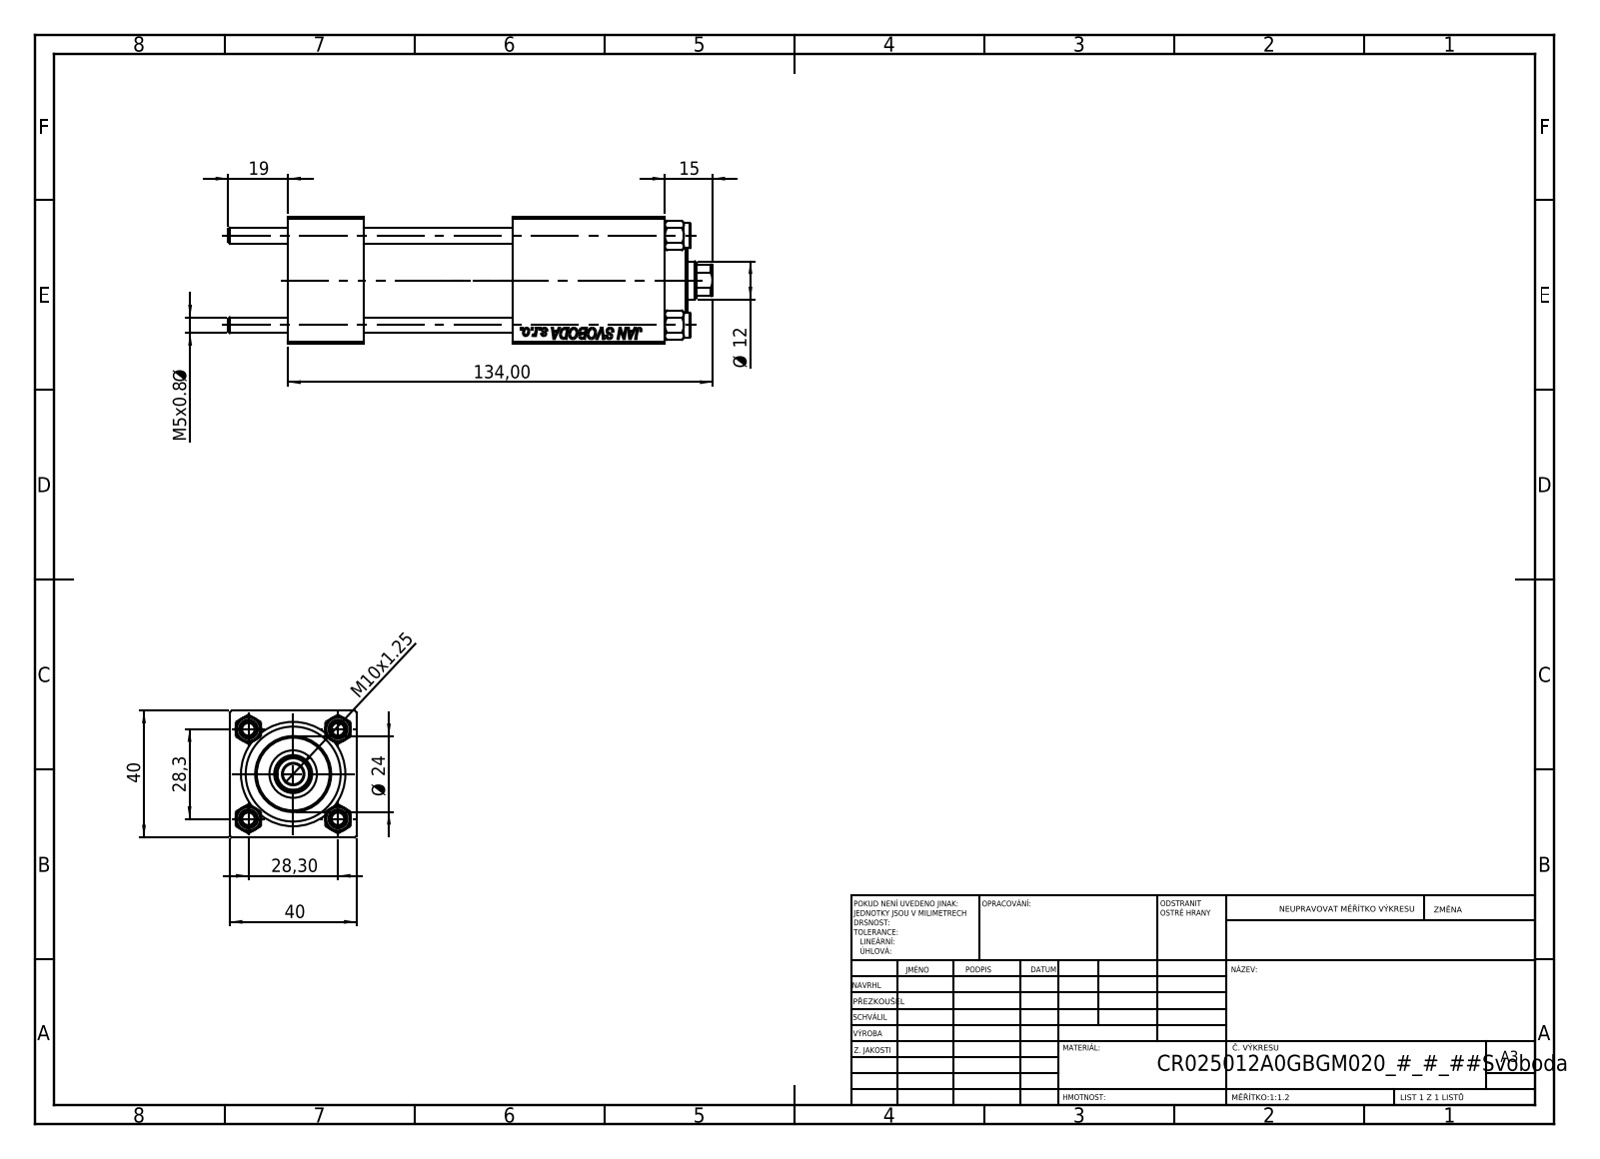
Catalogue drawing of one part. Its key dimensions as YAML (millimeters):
part_name: "NUT_M5; CR025_012_A_0_G_A_G_M_020_+#_##_TYCINKA; V215_VC_A; V215CR_VCP (+1 more)"
step_written_by: "SolidWorks 2019 (CONFIG_CONTROL_DESIGN)"
units: millimeters
bodies: {solids: 11, faces: 1131, planar: 517, cylindrical: 78, other: 536}
overall_size: [153, 40, 40]
volume: 145075
surface_area: 58807
round_holes:
  - {diameter: 5, count: 4}
  - {diameter: 20, count: 3}
  - {diameter: 7, count: 2}
  - {diameter: 13.16, count: 2}
  - {diameter: 6.5, count: 1}
  - {diameter: 12, count: 1}
  - {diameter: 15, count: 1}
  - {diameter: 25, count: 1}
  - {diameter: 30, count: 1}
round_bosses_or_shafts:
  - {diameter: 8, count: 4}
  - {diameter: 31, count: 1}
  - {diameter: 24, count: 1}
partial_cylinders:
  - {radius: 5.5, count: 1}
face_to_face_distances: [40, 24, 119, 95, 90.3, 66.3, 28.7, 71, 47, 19.3]
hole_center_spacings: [20.01, 28.3, 40.02, 72]
